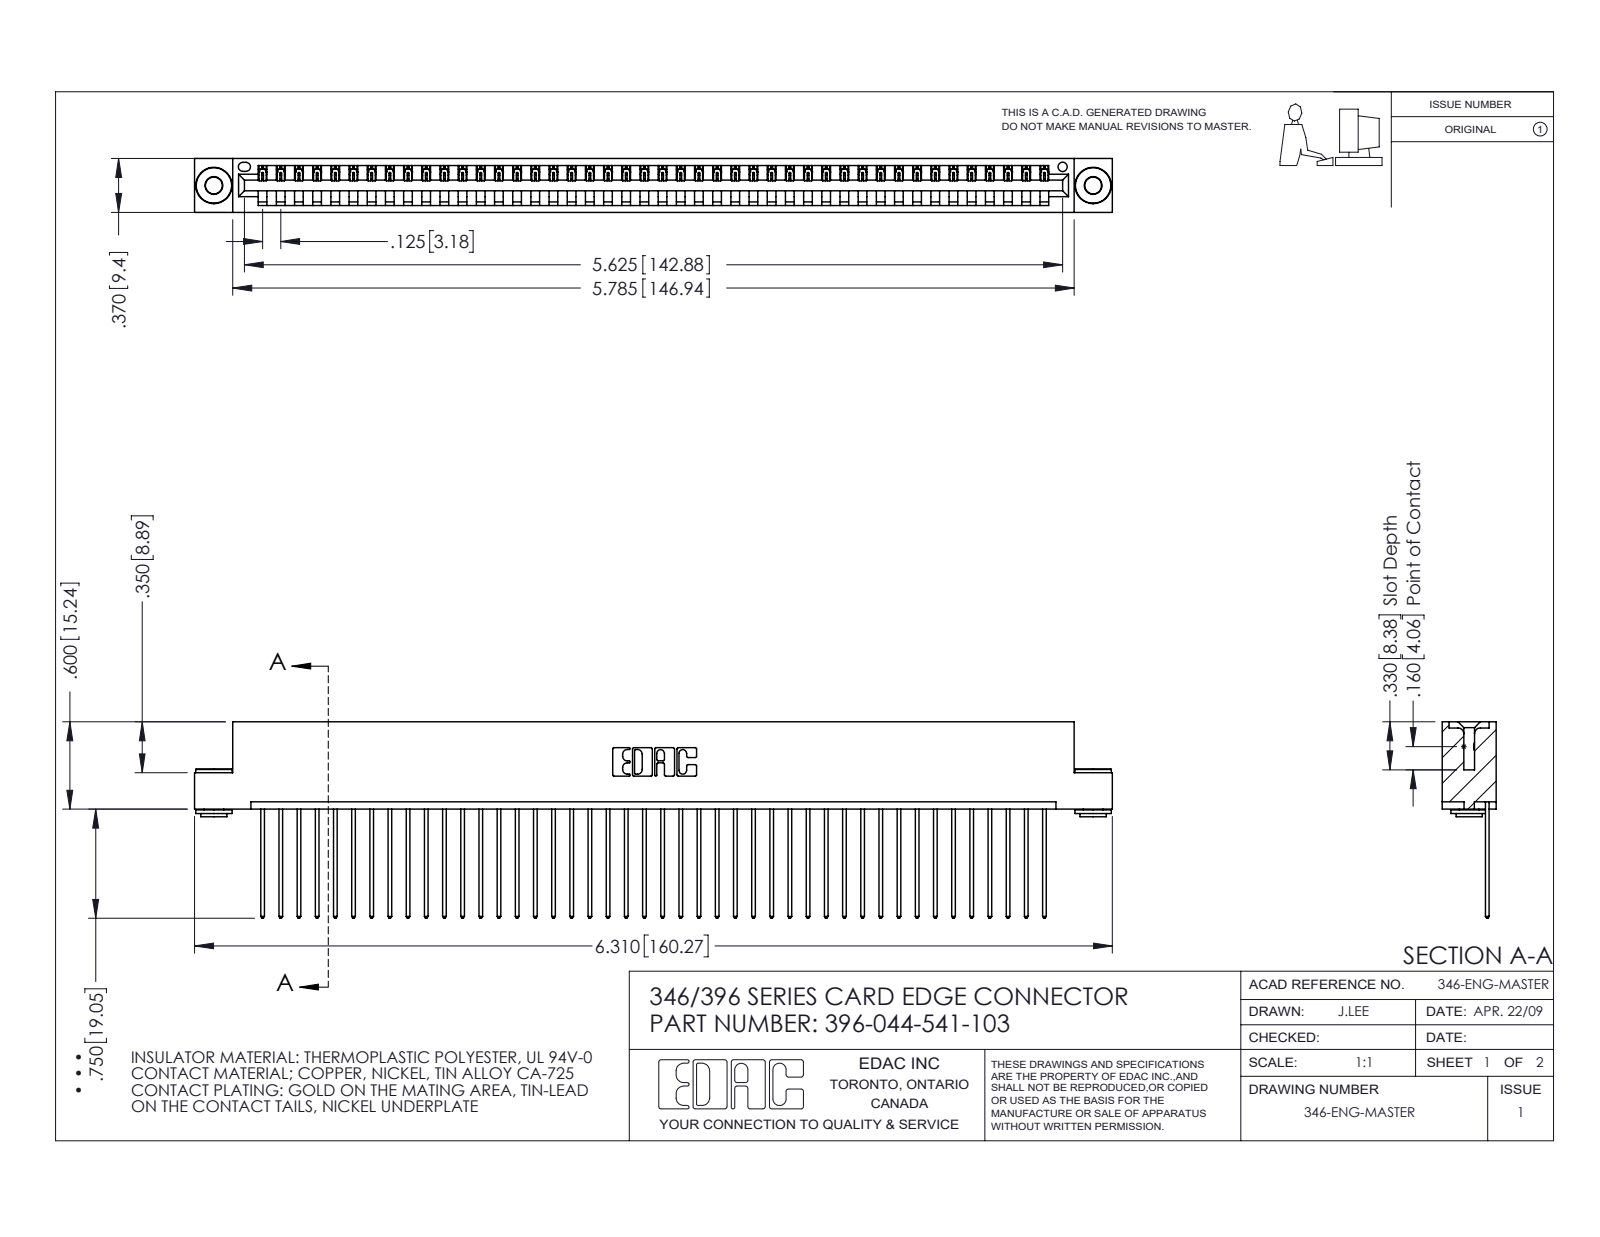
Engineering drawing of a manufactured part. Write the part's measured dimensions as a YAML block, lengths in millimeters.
part_name: "346 Part_Flush Mounting Lugs - 0.156 Dia-TH; 396-044-541-103; 345-250-002_345-250-002-102; 345-292-001_345-293-141"
step_written_by: "SolidWorks 2016 (CONFIG_CONTROL_DESIGN)"
units: millimeters
bodies: {solids: 47, faces: 2712, planar: 1846, cylindrical: 858, other: 8}
overall_size: [160.3, 34.3, 9.4]
volume: 15500
surface_area: 20500
round_holes:
  - {diameter: 2.9, count: 2}
  - {diameter: 4, count: 2}
  - {diameter: 1.6, count: 1}
round_bosses_or_shafts:
  - {diameter: 6.4, count: 2}
  - {diameter: 4.6, count: 2}
  - {diameter: 3.5, count: 2}
partial_cylinders:
  - {radius: 0.2, count: 88}
  - {radius: 0.3, count: 88}
  - {radius: 0.3, count: 22}
  - {radius: 0.2, count: 6}
  - {radius: 0.8, count: 6}
  - {radius: 0.7, count: 3}
  - {radius: 0.8, count: 2}
  - {radius: 1, count: 2}
face_to_face_distances: [1.2, 8.2, 9.4, 6.4, 0.6, 1.8, 7.6, 3.8, 5.6, 2.5]
hole_center_spacings: [6.2, 148.2, 153.5]
